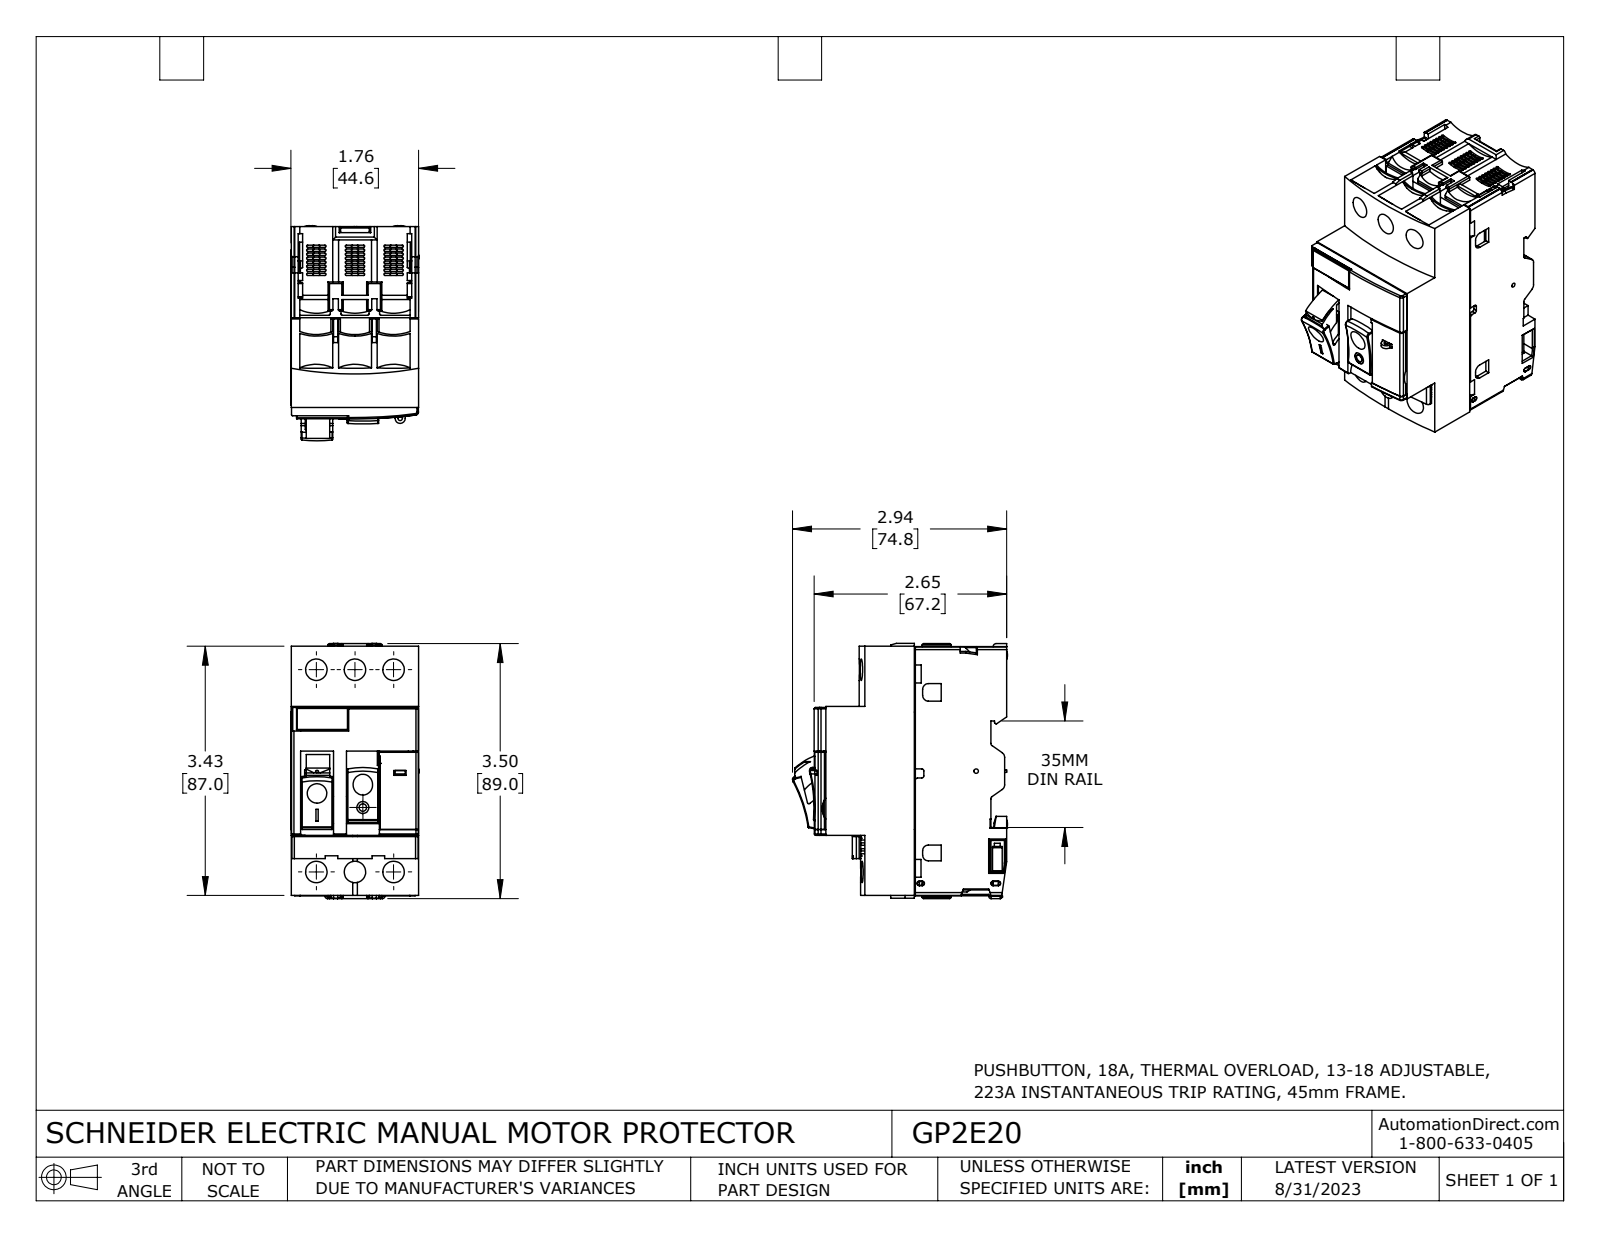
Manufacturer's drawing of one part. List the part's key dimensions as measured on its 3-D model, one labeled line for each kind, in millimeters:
Part name (STEP PRODUCT): GP2E20
STEP written by: SolidWorks 2021 (CONFIG_CONTROL_DESIGN)
Units: millimetres
Bodies: 15 solids, 2269 faces (1521 planar, 657 cylindrical, 91 other)
Overall size (bounding box): 89.1 × 75.1 × 44.8
Volume: 189 800 mm³ · Surface area: 63 830 mm²
Round holes (diameter × count): ⌀7.5 ×6, ⌀5 ×5, ⌀1.5 ×2, ⌀4 ×1, ⌀4.2 ×1, ⌀8 ×1, ⌀8.3 ×1, ⌀8.5 ×1, ⌀8.7 ×1
Round bosses / shafts (diameter × count): ⌀6.2 ×2, ⌀3 ×2, ⌀9.7 ×1, ⌀2.6 ×1, ⌀1.2 ×1
Partial cylindrical surfaces — rounded edges, fillets, slot ends (radius × count): R0.4 ×104, R0.5 ×47, R1 ×16, R0.3 ×12, R0.3 ×12, R0.8 ×12, R1.5 ×8, R0.1 ×6
Main face-to-face distances: 44.5, 13.5, 2.9, 31.3, 44.6, 1.5, 41.6, 14.8, 26.7, 29.7
Hole centre spacings: 13.5, 71.9, 70.6, 8.8, 10.2, 13.9, 17, 18.4
